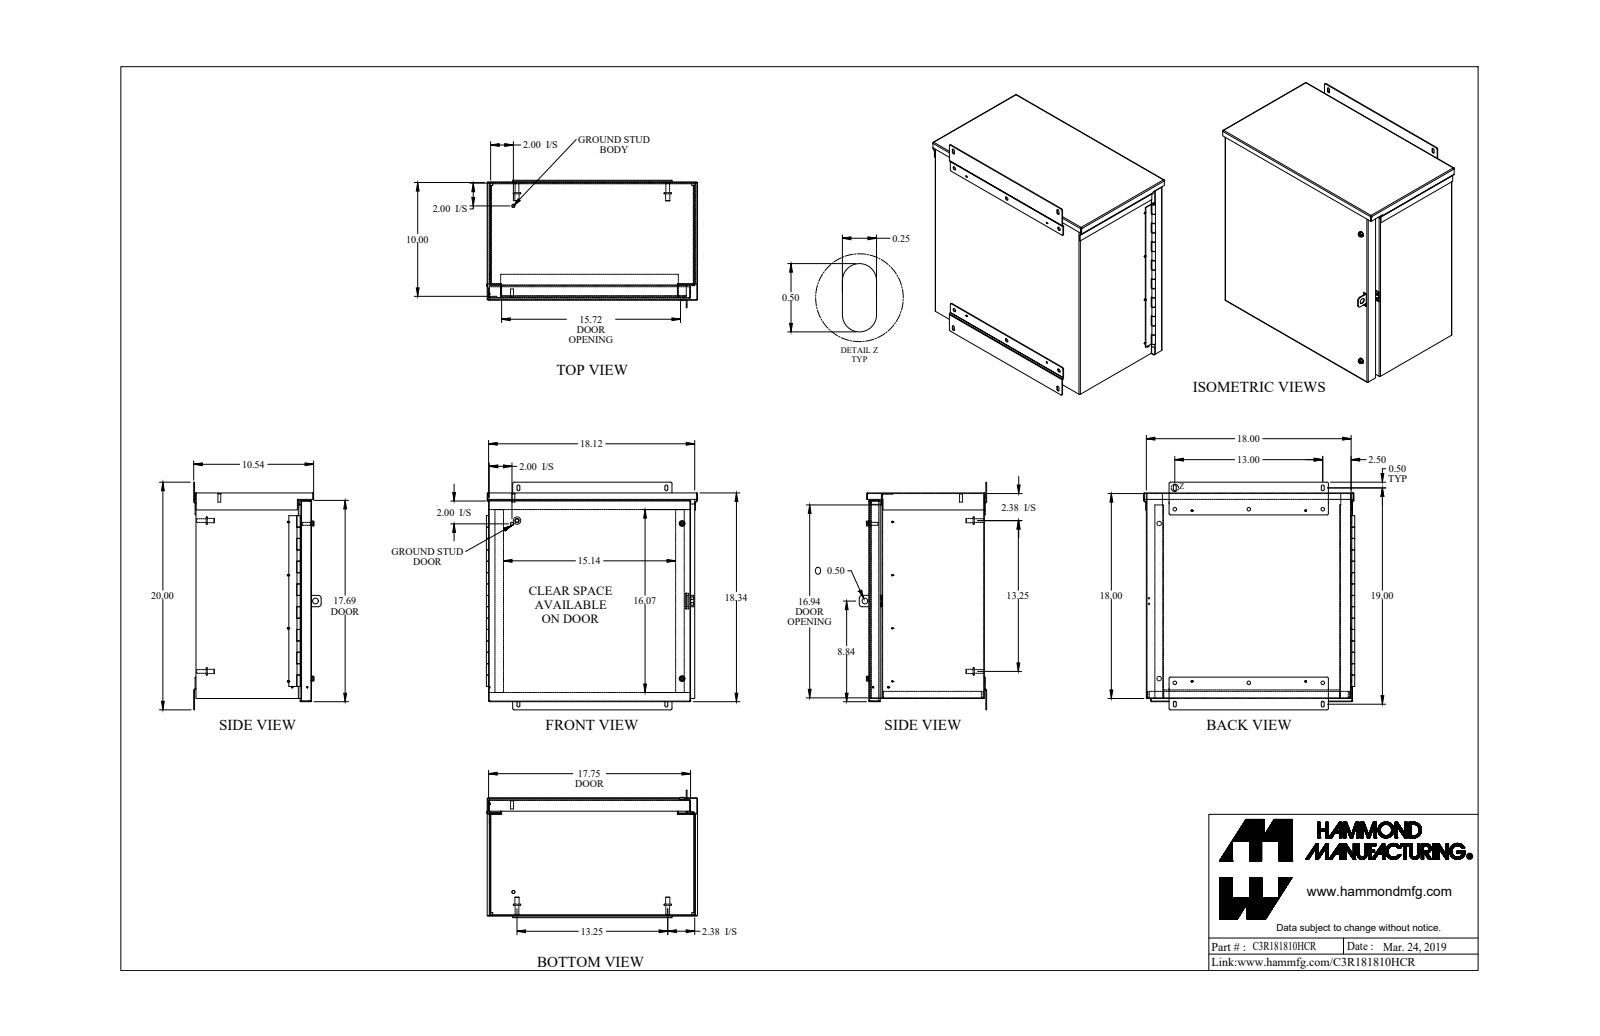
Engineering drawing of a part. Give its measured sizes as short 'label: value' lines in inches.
name: C3R181810HCR_Default
written by: SolidWorks 2019 (CONFIG_CONTROL_DESIGN)
unit: in
bodies: 33 solids, 846 faces (481 planar, 311 cylindrical, 54 other)
size: 20 × 18.556 × 11.197
volume: 109.9 in³; area: 3 614 in²
holes: 9× ⌀0.313, 4× ⌀0.14, 3× ⌀0.26, 2× ⌀0.137, 2× ⌀0.266, 2× ⌀0.28, 2× ⌀0.29, 2× ⌀0.397, 1× ⌀0.188, 1× ⌀0.5
bosses: 10× ⌀0.131, 4× ⌀0.65, 4× ⌀0.375, 4× ⌀0.33, 3× ⌀0.51, 3× ⌀0.244, 3× ⌀0.187, 2× ⌀0.5
rounds: 26× R0.029, 26× R0.086, 19× R0.125, 5× R0.036, 5× R0.108, 3× R0.171, 2× R0.25
face distances: 0.057, 10.1, 18, 17.943, 10.043, 10.157, 18.057, 17.886, 1, 0.943
hole spacings: 1.505, 5.002, 6.5, 11.501, 15.93, 19, 15.199, 16.577
